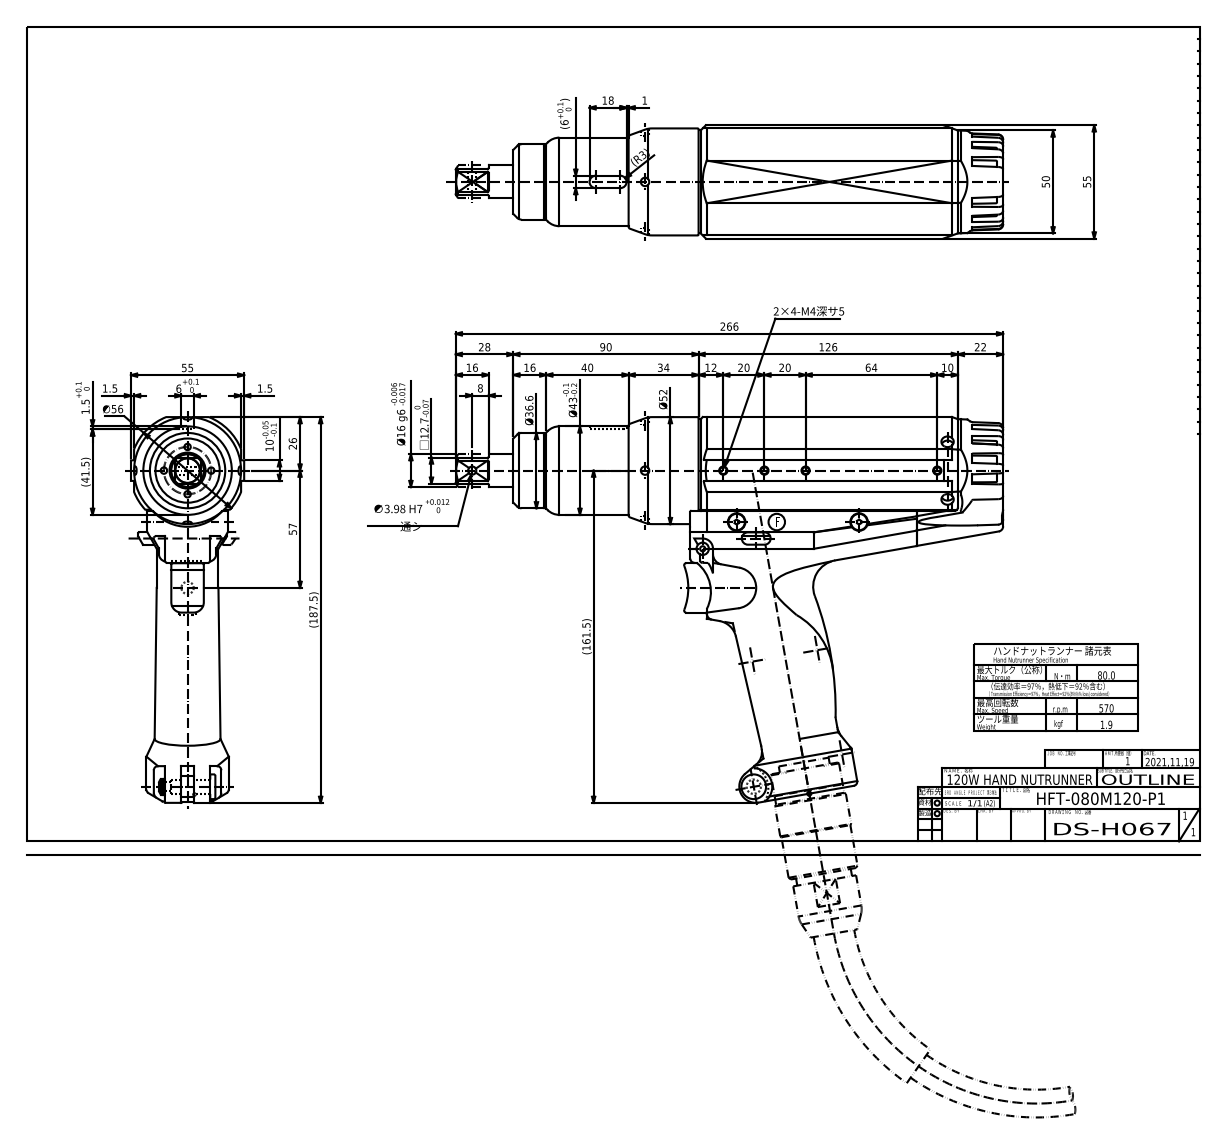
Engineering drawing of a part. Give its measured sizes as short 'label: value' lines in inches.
name: HFT-080M120-P1(DS-H067)_OUTLINE_20221021
written by: Autodesk Inventor 2021 (AUTOMOTIVE_DESIGN)
unit: in
bodies: 1 solid, 1586 faces (677 planar, 346 cylindrical, 563 other)
size: 10.472 × 7.38 × 2.165
volume: 39.54 in³; area: 171.6 in²
holes: 7× ⌀0.236, 5× ⌀0.128, 4× ⌀0.122, 2× ⌀0.161, 2× ⌀0.228, 2× ⌀0.335, 1× ⌀0.098, 1× ⌀0.126, 1× ⌀0.157, 1× ⌀0.177, 1× ⌀0.315, 1× ⌀0.394
bosses: 24× ⌀0.039, 5× ⌀0.217, 4× ⌀0.063, 3× ⌀0.228, 2× ⌀1.016, 2× ⌀0.315, 2× ⌀0.118, 2× ⌀0.031
rounds: 30× R0.02, 14× R0.039, 7× R0.236, 6× R0.012, 5× R0.079, 5× R0.098, 5× R0.118, 4× R0.102
face distances: 0.059, 2.106, 0.118, 0.315, 1.791, 0.591, 0.138, 2.146, 0.256, 0.453
hole spacings: 0.453, 0.64, 0.787, 0.906, 1.017, 1.119, 2.289, 3.307
